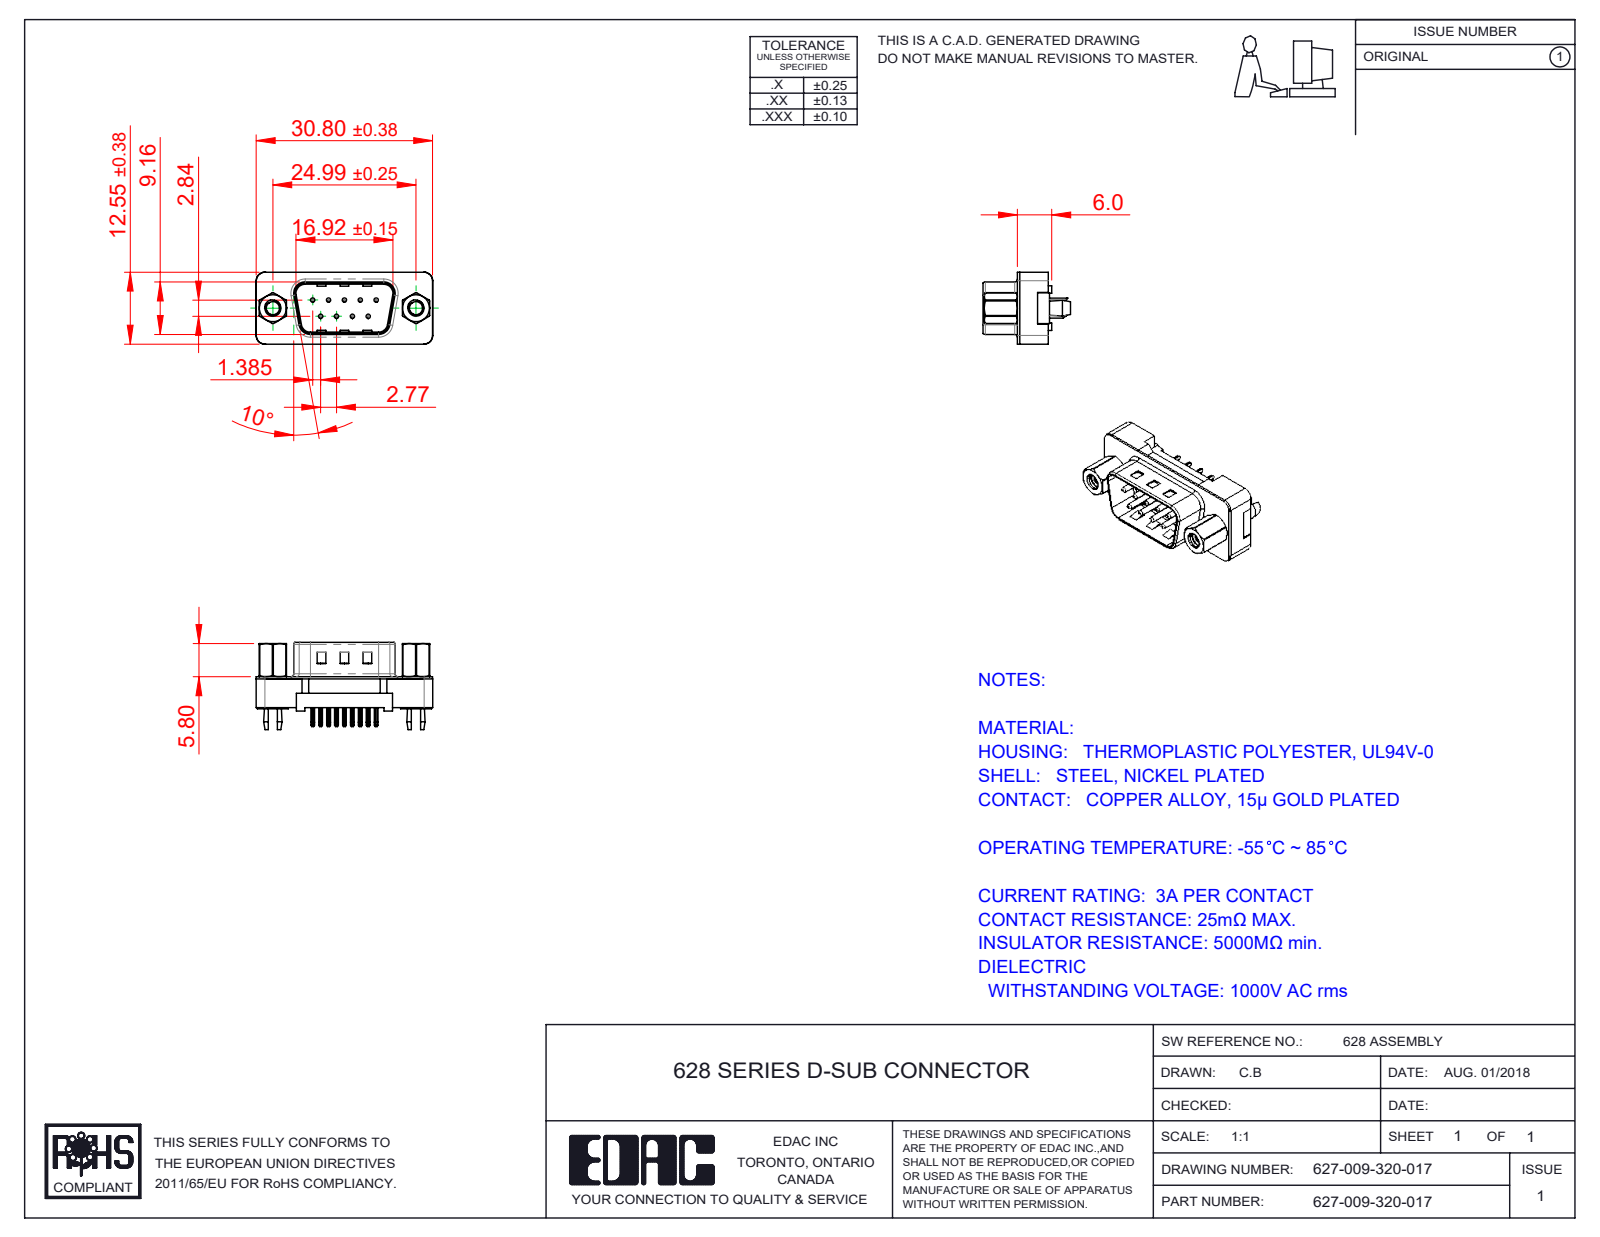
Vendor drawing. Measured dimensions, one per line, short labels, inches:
name: 627 PB Contact Row 2_20; 627 PB 4-40 Threaded Rivet with Boardlock; 627 PB Shell_09 Contacts; 627-009-320-017 (+3 more)
written by: SolidWorks 2020 (CONFIG_CONTROL_DESIGN)
unit: in
bodies: 15 solids, 925 faces (513 planar, 306 cylindrical, 106 other)
size: 1.213 × 0.6 × 0.494
volume: 0.115 in³; area: 6.07 in²
holes: 9× ⌀0.014, 9× ⌀0.033, 2× ⌀0.089, 2× ⌀0.09, 2× ⌀0.157, 2× ⌀0.189, 2× ⌀0.197
bosses: 9× ⌀0.03, 2× ⌀0.193, 2× ⌀0.11
rounds: 18× R0.01, 9× R0.005, 8× R0.02, 7× R0.059, 4× R0.035, 4× R0.063, 4× R0.079, 2× R0.016
face distances: 0.016, 0.098, 0.213, 0.197, 0.062, 0.083, 0.138, 0.114, 0.345, 0.075
hole spacings: 0.124, 0.109, 0.198, 0.218, 0.295, 0.198, 0.279, 0.327
